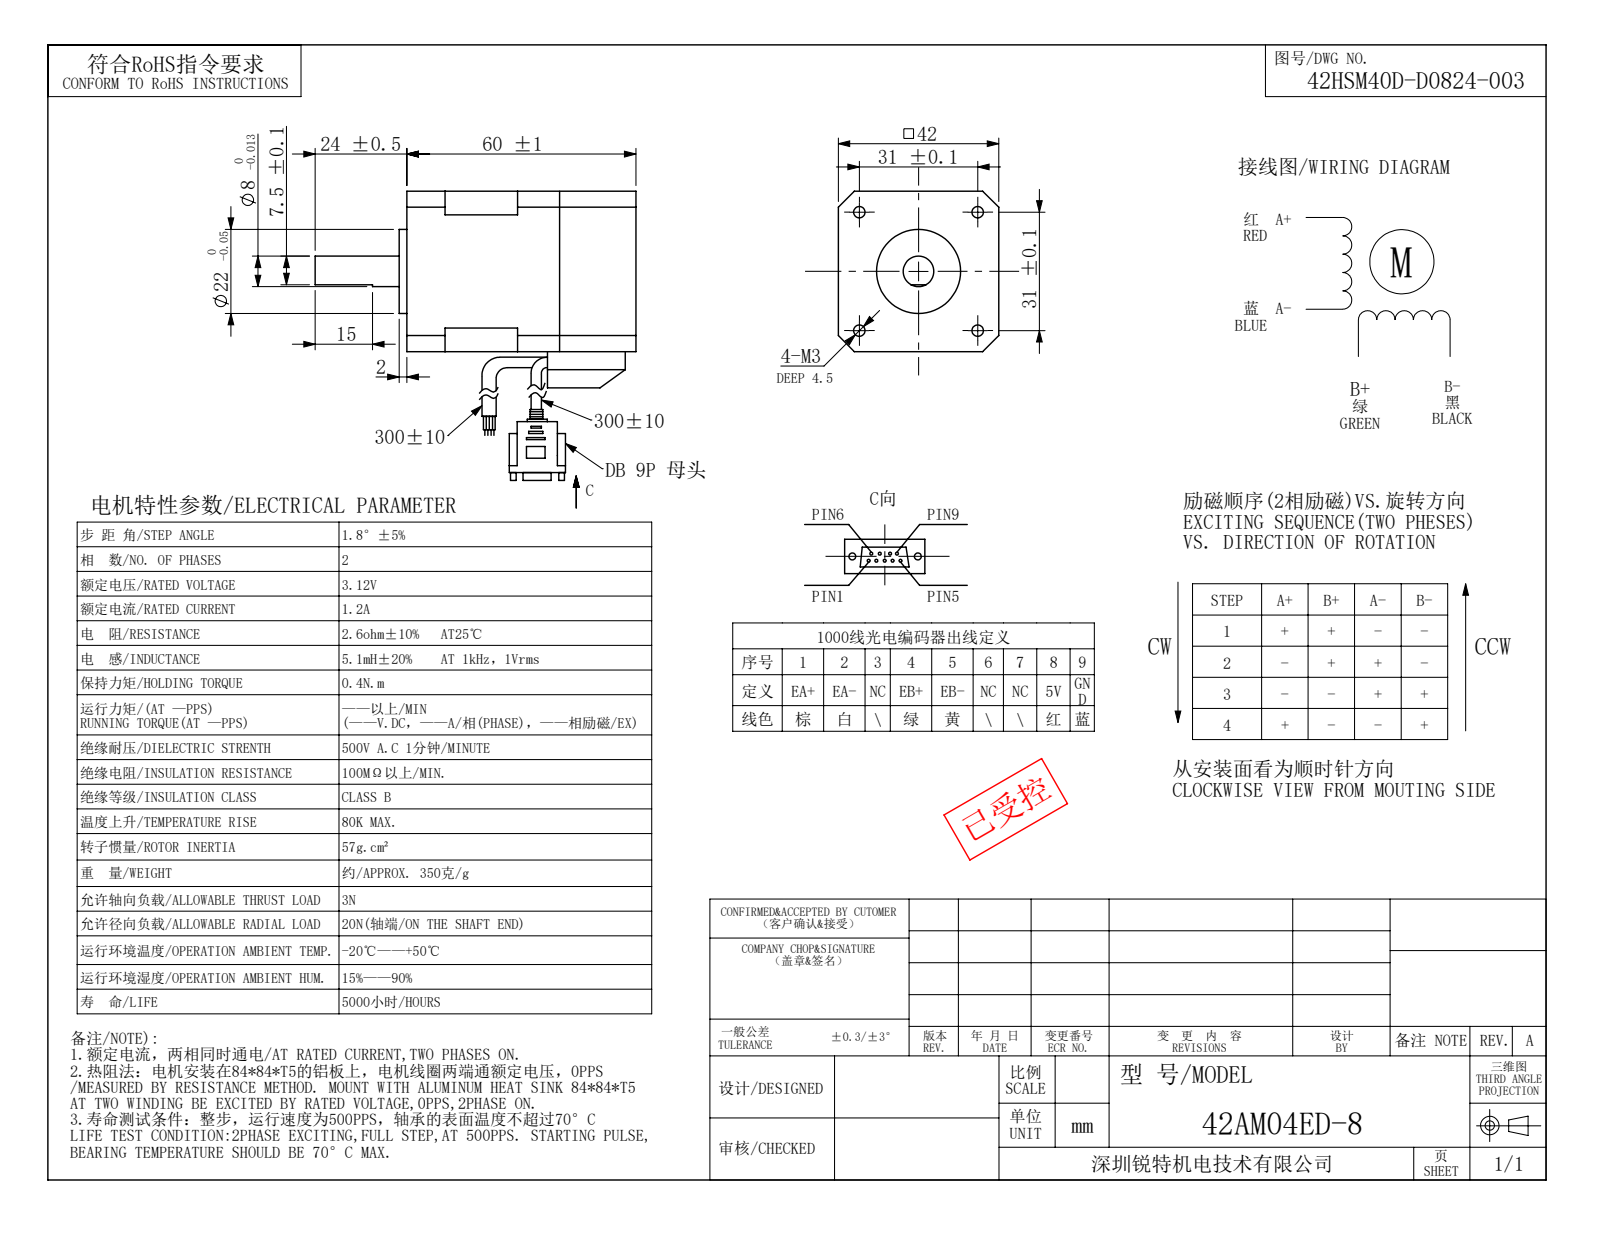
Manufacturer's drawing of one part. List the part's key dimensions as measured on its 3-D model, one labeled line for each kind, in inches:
STEP written by: SolidWorks 2014 (AUTOMOTIVE_DESIGN)
Units: inches
Bodies: 1 solid, 46 faces (34 planar, 12 cylindrical, 0 other)
Overall size (bounding box): 3.307 × 1.654 × 1.654
Volume: 6.325 in³ · Surface area: 23.46 in²
Round holes (diameter × count): ⌀0.118 ×4
Round bosses / shafts (diameter × count): ⌀0.866 ×1, ⌀0.315 ×1
Main face-to-face distances: 1.654, 2.362, 0.056, 2.048, 1.993, 2.441, 0.079, 2.104, 2.104, 2.049
Hole centre spacings: 1.22, 1.726
